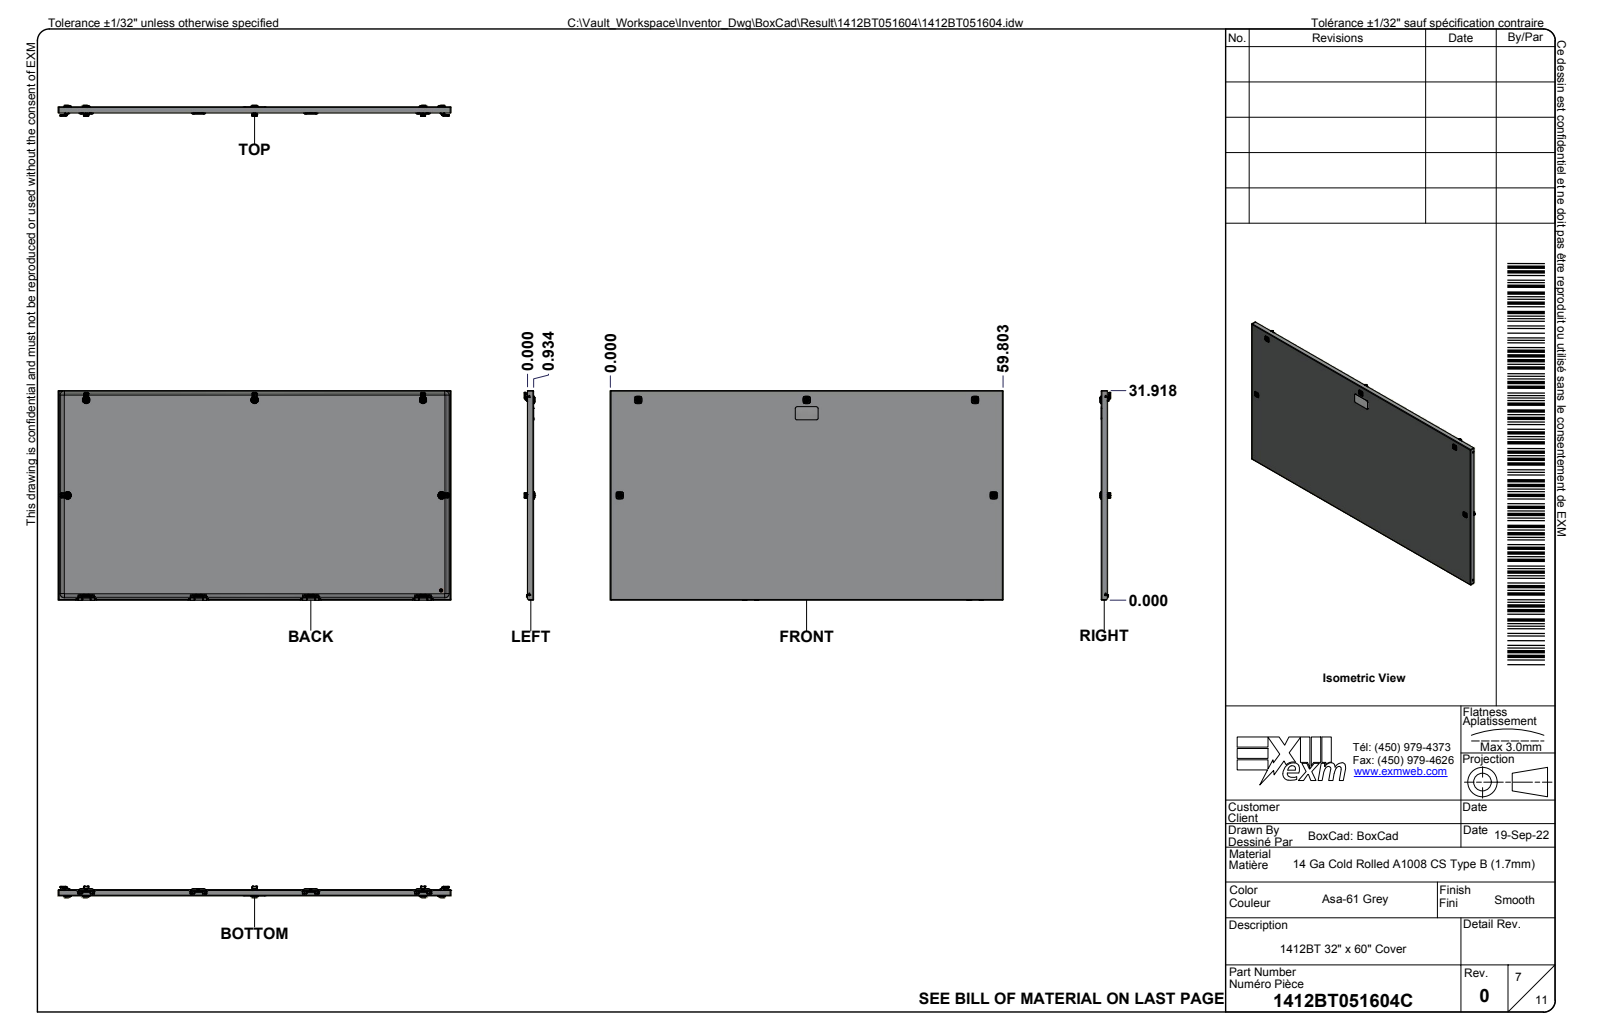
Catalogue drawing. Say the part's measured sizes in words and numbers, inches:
The part is named "1412BT051604; 1412BT051604B; 1412BT051604B-P; STK-Q-16005 (+8 more)". Its 3-D file was written by "Autodesk Inventor 2024 (AUTOMOTIVE_DESIGN)". It is 216 solids with 32882 faces: 12641 planar, 7960 cylindrical and 12281 other. Overall it measures 60 by 34.25 by 13.588 inches. Its volume is 1 124 cubic inches and its surface area 18 687 square inches. Round holes: 48 of diameter 0.177, 24 of diameter 0.453, 18 of diameter 0.27, 16 of diameter 0.043, 12 of diameter 0.262, 12 of diameter 0.562, 12 of diameter 0.571, 10 of diameter 0.03, 10 of diameter 0.315, 9 of diameter 0.201, 8 of diameter 0.178, 5 of diameter 0.311. Round bosses or shafts: 16 of diameter 0.472, 16 of diameter 0.039, 12 of diameter 0.307, 11 of diameter 0.232, 10 of diameter 0.03, 9 of diameter 0.571, 8 of diameter 0.311, 8 of diameter 0.262. Partial cylindrical surfaces (rounded edges, fillets, slot ends): 565 of radius 0.02, 368 of radius 0.031, 323 of radius 0.039, 305 of radius 0.01, 218 of radius 0.008, 164 of radius 0.012, 110 of radius 0.004, 110 of radius 0.016. The main face-to-face distances are 0.068, 13.052, 12.983, 13.12, 1.828, 31.932, 0.068, 1.01, 0.942, 12.042. The hole center spacings are 0.61, 16.5, 17.11, 17.896, 15.89, 33.72, 17.101, 34.202.
